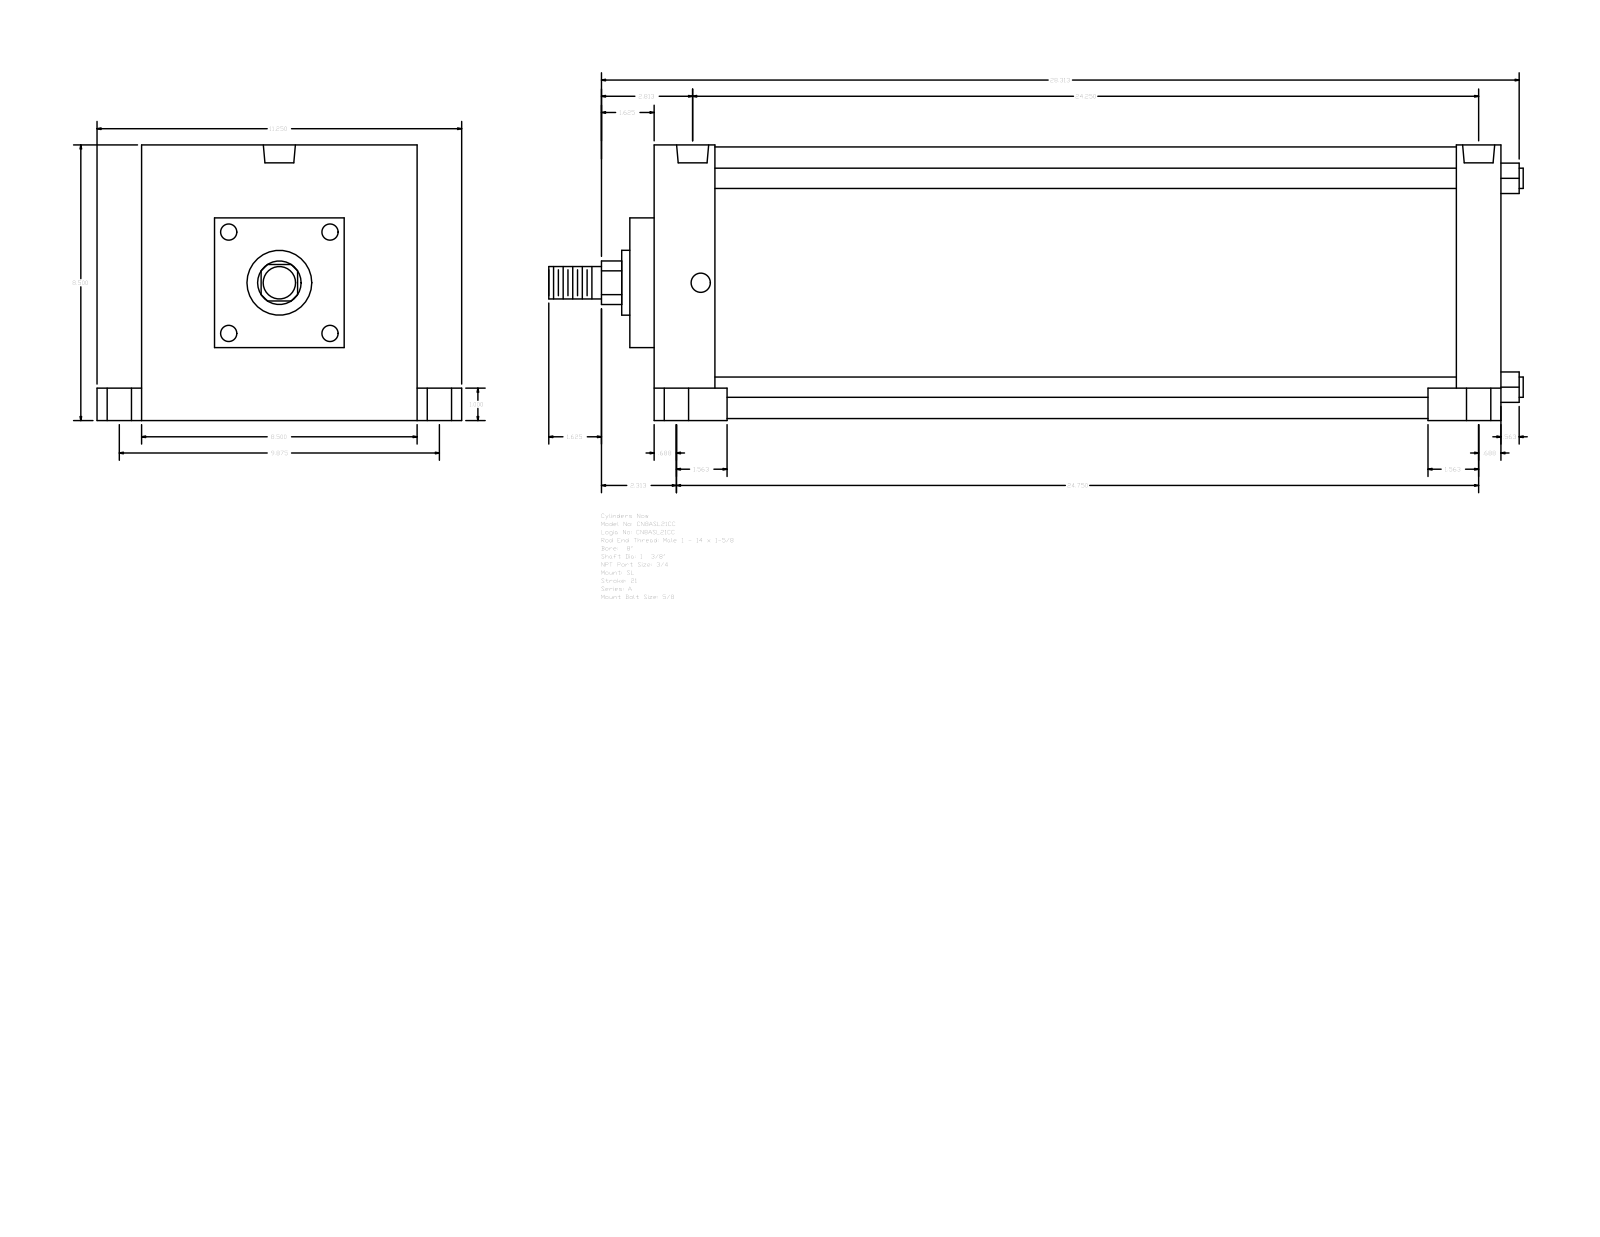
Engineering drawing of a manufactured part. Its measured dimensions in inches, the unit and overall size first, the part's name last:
Units: inches
Overall size (bounding box): 30.063 × 11.25 × 8.5
Round holes (diameter × count): ⌀0.594 ×4, ⌀0.75 ×4, ⌀1 ×4, ⌀0.989 ×2
Round bosses / shafts (diameter × count): ⌀0.625 ×4, ⌀8.375 ×1, ⌀2 ×1, ⌀1.375 ×1, ⌀1 ×1
Partial cylindrical surfaces — rounded edges, fillets, slot ends (radius × count): R0.672 ×1
Main face-to-face distances: 26.125, 8.5, 1.375, 2.25, 1.875, 24.25, 24.75, 22.875, 0.75, 2.625
Hole centre spacings: 0.25, 4.937, 4.944, 4.963, 4.994, 9.875, 23.75, 24
Bodies: 0 solids, 117 faces (85 planar, 32 cylindrical, 0 other)
Part name (STEP PRODUCT): A_SL__0800_1.375
STEP written by: GSSL Pune (CONFIG_CONTROL_DESIGN)
